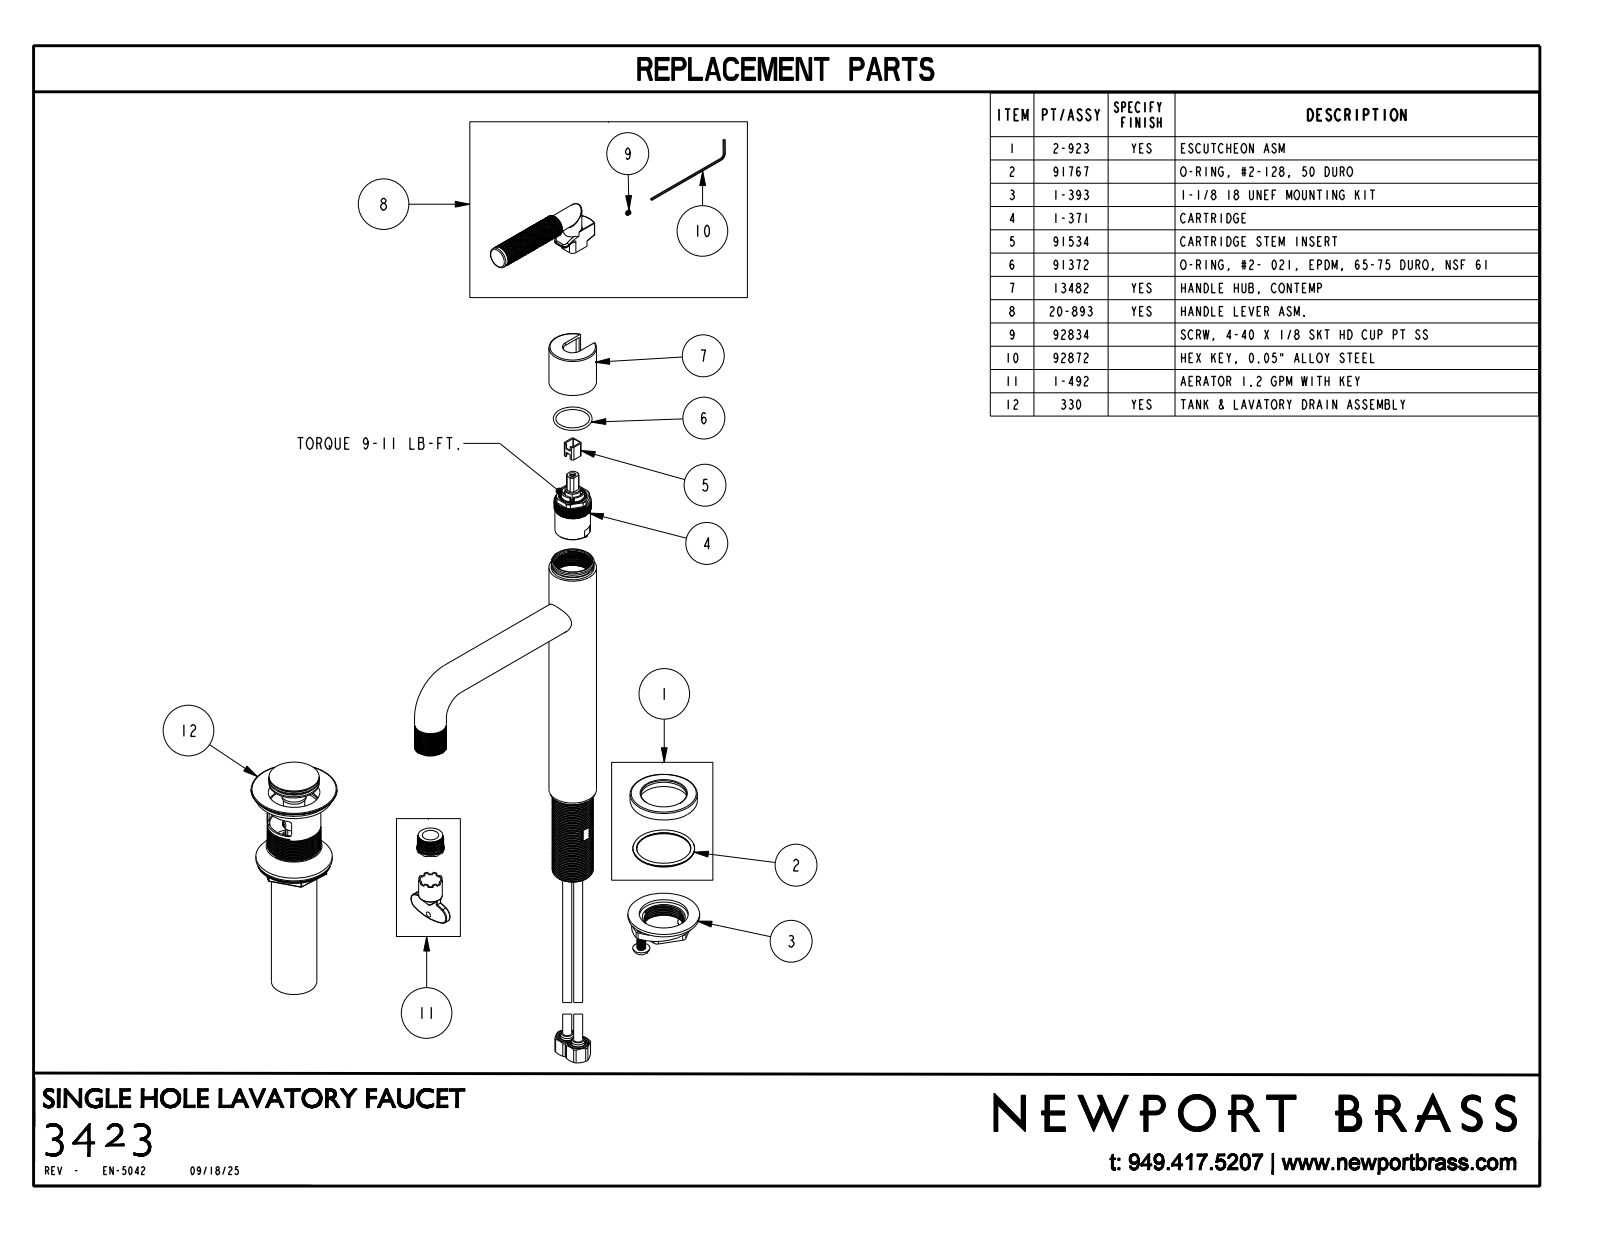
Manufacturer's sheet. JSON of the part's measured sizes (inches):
{"part_name": "3423", "step_written_by": "CREO PARAMETRIC BY PTC INC, 2025093 (CONFIG_CONTROL_DESIGN)", "units": "inches", "bodies": {"solids": 1, "faces": 9498, "planar": 40, "cylindrical": 1954, "other": 7504}, "overall_size": [9.68, 6.939, 1.85], "volume_in3": 16.83, "surface_area_in2": 73.79, "round_holes": [[0.764, 1], [1.2, 1]], "round_bosses_or_shafts": [[0.875, 2], [0.5, 2], [1.85, 1], [1.31, 1], [1.175, 1], [0.59, 1], [0.236, 1]], "partial_cylinders_radius": [[0.01, 8], [0.015, 6], [0.03, 6], [0.156, 6], [0.031, 4], [0.125, 4], [0.05, 1], [0.275, 1]], "face_to_face_distances": [0.25, 8.226, 7.976, 0.7, 8.926, 8.676, 0.014, 0.58, 8.24, 7.99], "hole_center_spacings": [5.576]}
